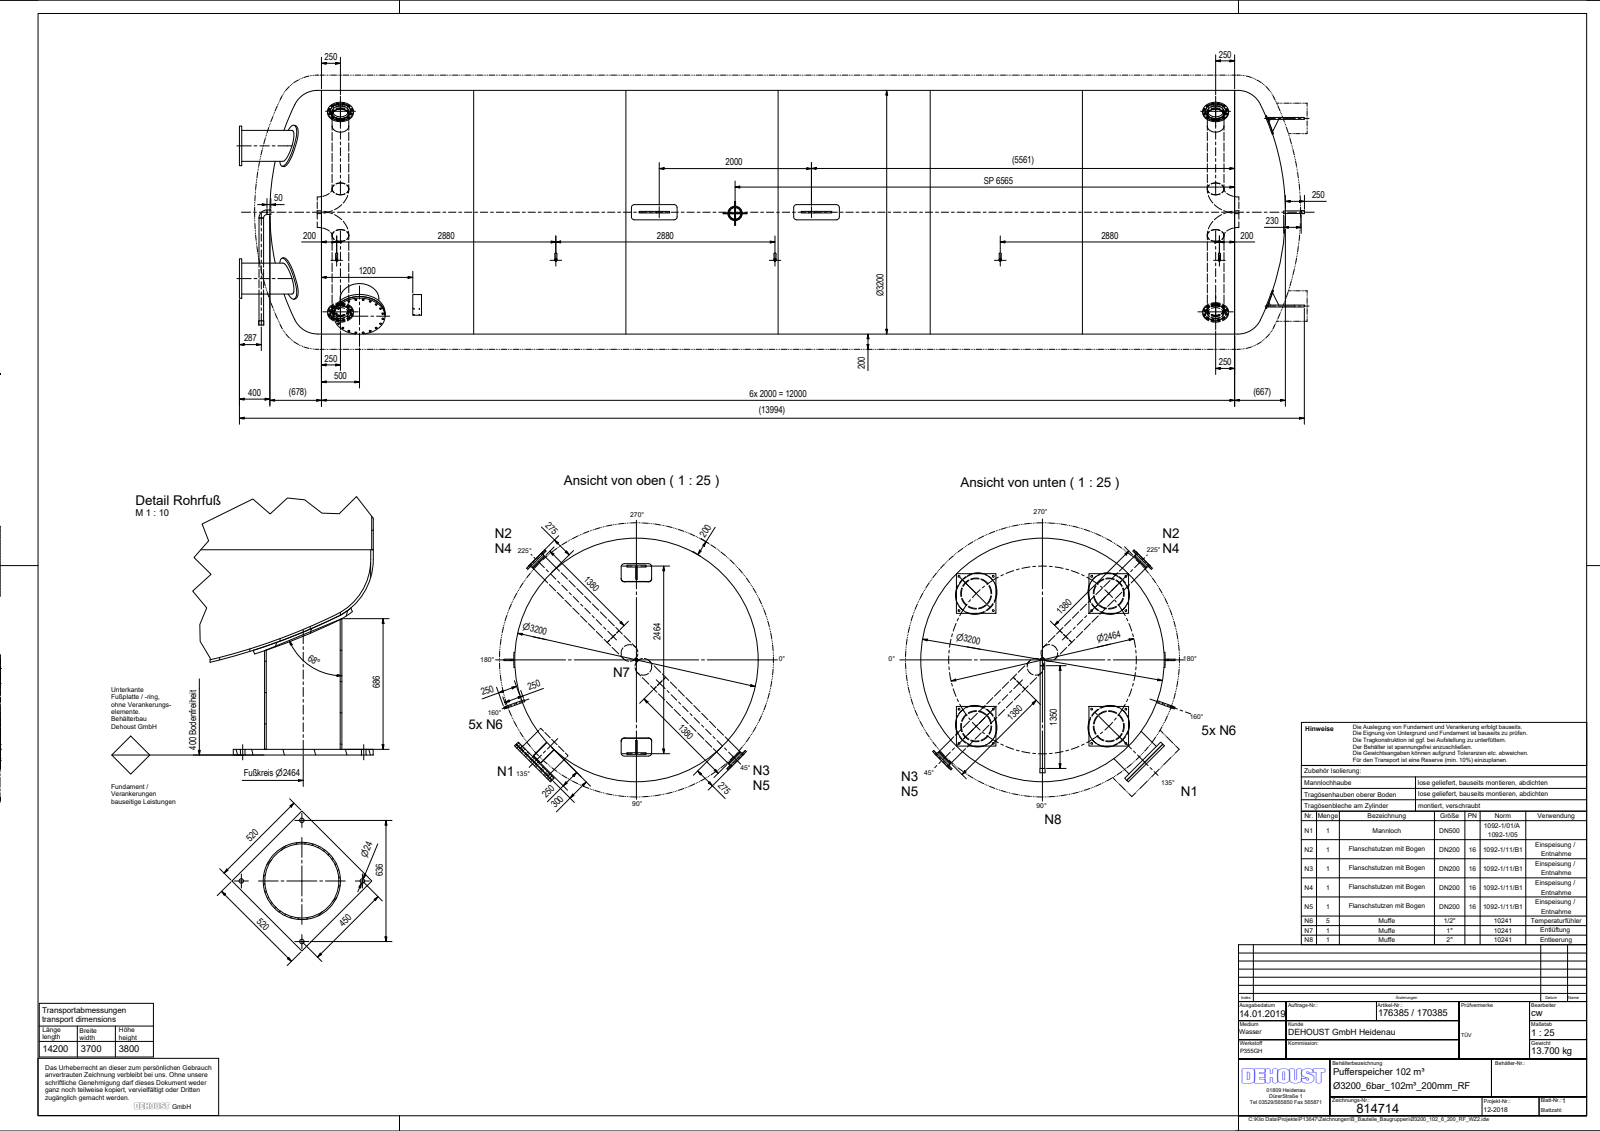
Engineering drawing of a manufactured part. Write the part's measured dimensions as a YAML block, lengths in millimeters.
part_name: "Ø3200_102_6_200_RF_WZ2; Klöpper_Gew_Ø3200_10,6; Klöpper_Gew_Ø3200_13,0; Zyl_Ø3200_8x12000_2019 (+8 more)"
step_written_by: "Autodesk Inventor 2019 (AUTOMOTIVE_DESIGN)"
units: millimeters
bodies: {solids: 58, faces: 457, planar: 176, cylindrical: 231, other: 50}
overall_size: [13995.52, 3342.95, 3202.3]
volume: 1660000000
surface_area: 312000000
round_holes:
  - {diameter: 22, count: 48}
  - {diameter: 26, count: 40}
  - {diameter: 24, count: 16}
  - {diameter: 18.63, count: 5}
  - {diameter: 21.7, count: 5}
  - {diameter: 26.9, count: 5}
  - {diameter: 5.8, count: 4}
  - {diameter: 206.5, count: 4}
  - {diameter: 207.3, count: 4}
  - {diameter: 219.1, count: 4}
  - {diameter: 388.8, count: 4}
  - {diameter: 52.3, count: 2}
round_bosses_or_shafts:
  - {diameter: 219.1, count: 8}
  - {diameter: 26.9, count: 5}
  - {diameter: 26.4, count: 5}
  - {diameter: 560, count: 4}
  - {diameter: 406.4, count: 4}
  - {diameter: 340, count: 4}
  - {diameter: 268, count: 4}
  - {diameter: 670, count: 2}
partial_cylinders:
  - {radius: 40, count: 8}
  - {radius: 42, count: 8}
  - {radius: 5, count: 2}
  - {radius: 10, count: 2}
  - {radius: 72, count: 2}
  - {radius: 125, count: 1}
  - {radius: 1612, count: 1}
face_to_face_distances: [30, 600, 5582.5, 6417.5, 6660.78, 7495.78, 6630.78, 7465.78, 835, 28]
hole_center_spacings: [147.5, 310, 191.59, 501.59, 147.49, 2880, 364.43, 589.65]
